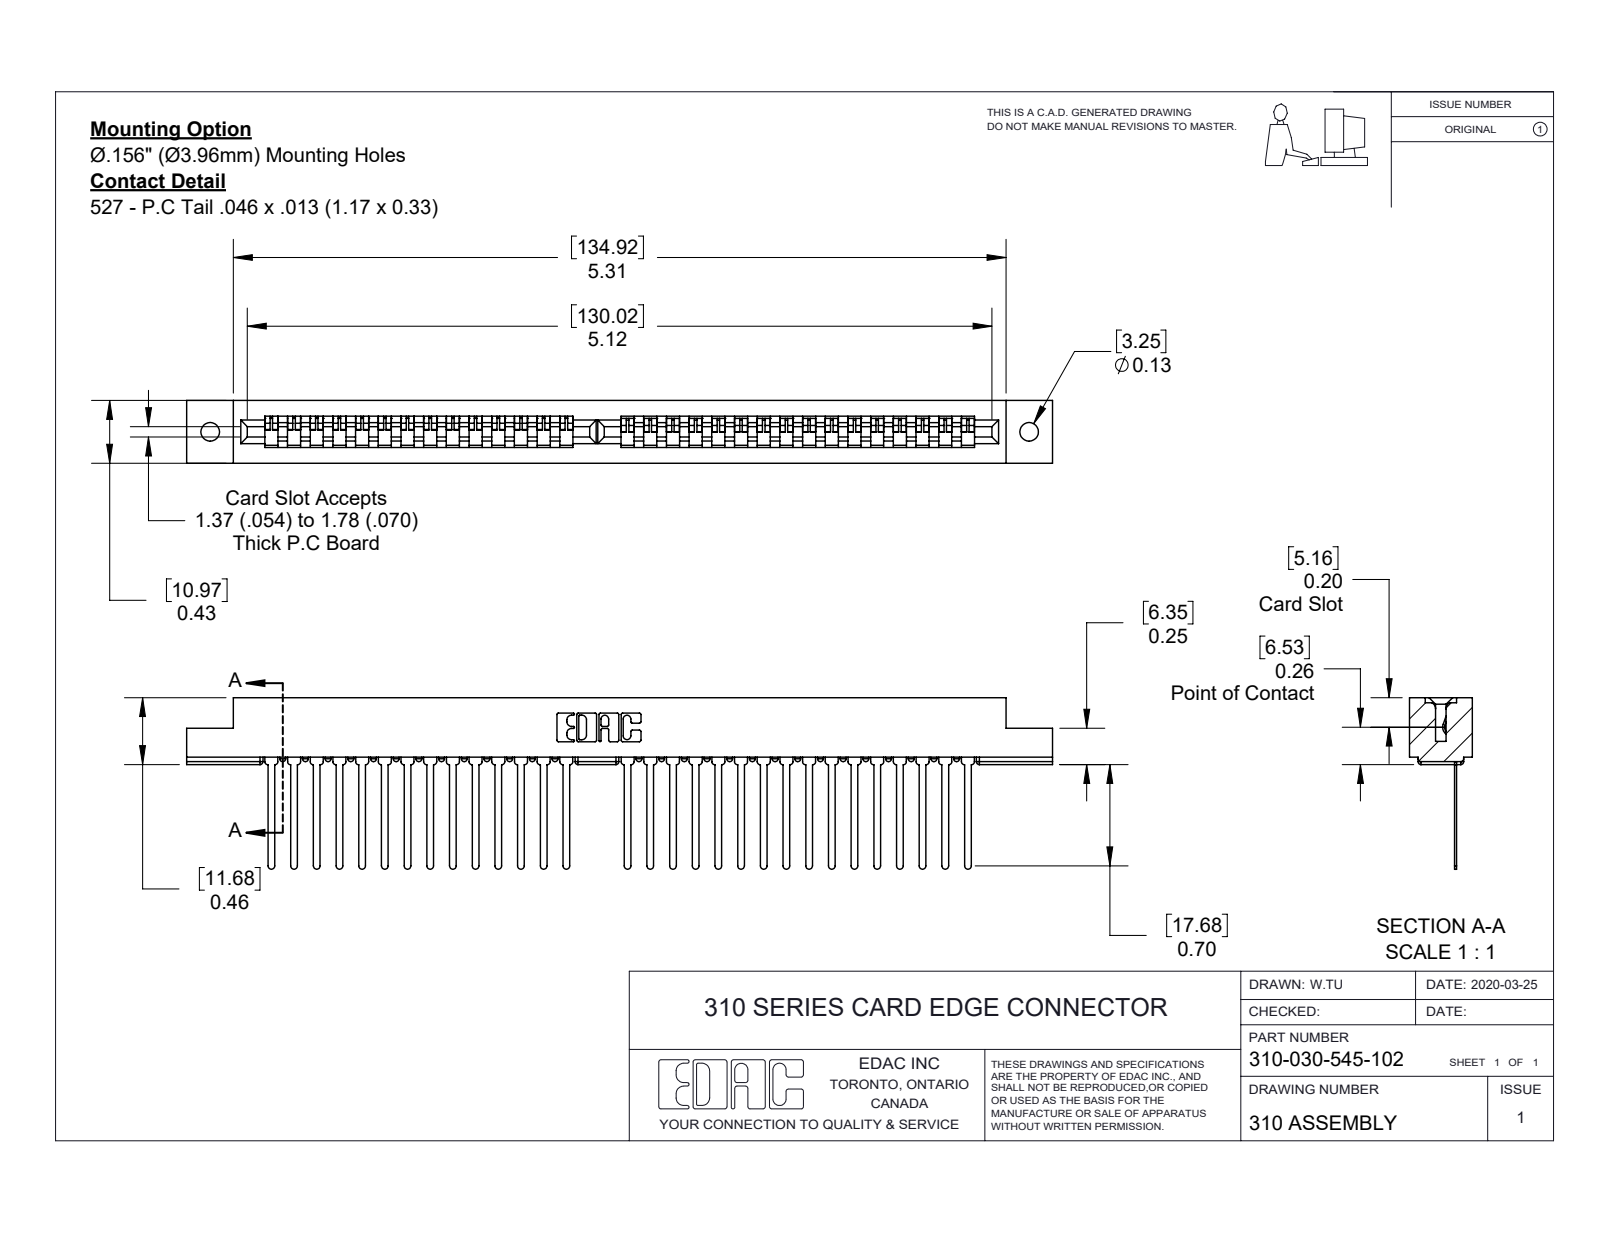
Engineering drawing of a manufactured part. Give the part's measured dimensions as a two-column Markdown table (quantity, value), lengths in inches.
| quantity | value |
| --- | --- |
| part name | 310 Part_.128 Dia. Hole; 307-290-001_545; 310-030-545-102 |
| STEP written by | SolidWorks 2016 (CONFIG_CONTROL_DESIGN) |
| units | inches |
| bodies | 31 solids, 1846 faces (1194 planar, 588 cylindrical, 64 other) |
| overall size | 5.953 × 1.179 × 0.432 |
| volume | 0.778 in³ |
| surface area | 24.26 in² |
| round holes (diameter × count) | 0.128 × 2 |
| partial cylindrical surfaces (radius × count) | 0.02 × 158, 0.023 × 30, 0.01 × 22, 0.007 × 6, 0.031 × 6, 0.026 × 3, 0.012 × 2, 0.025 × 2 |
| main face-to-face distances | 0.109, 0.324, 0.015, 0.013, 0.432, 0.072, 0.124, 0.309, 0.2, 0.409 |
| hole center spacings | 5.63 |
